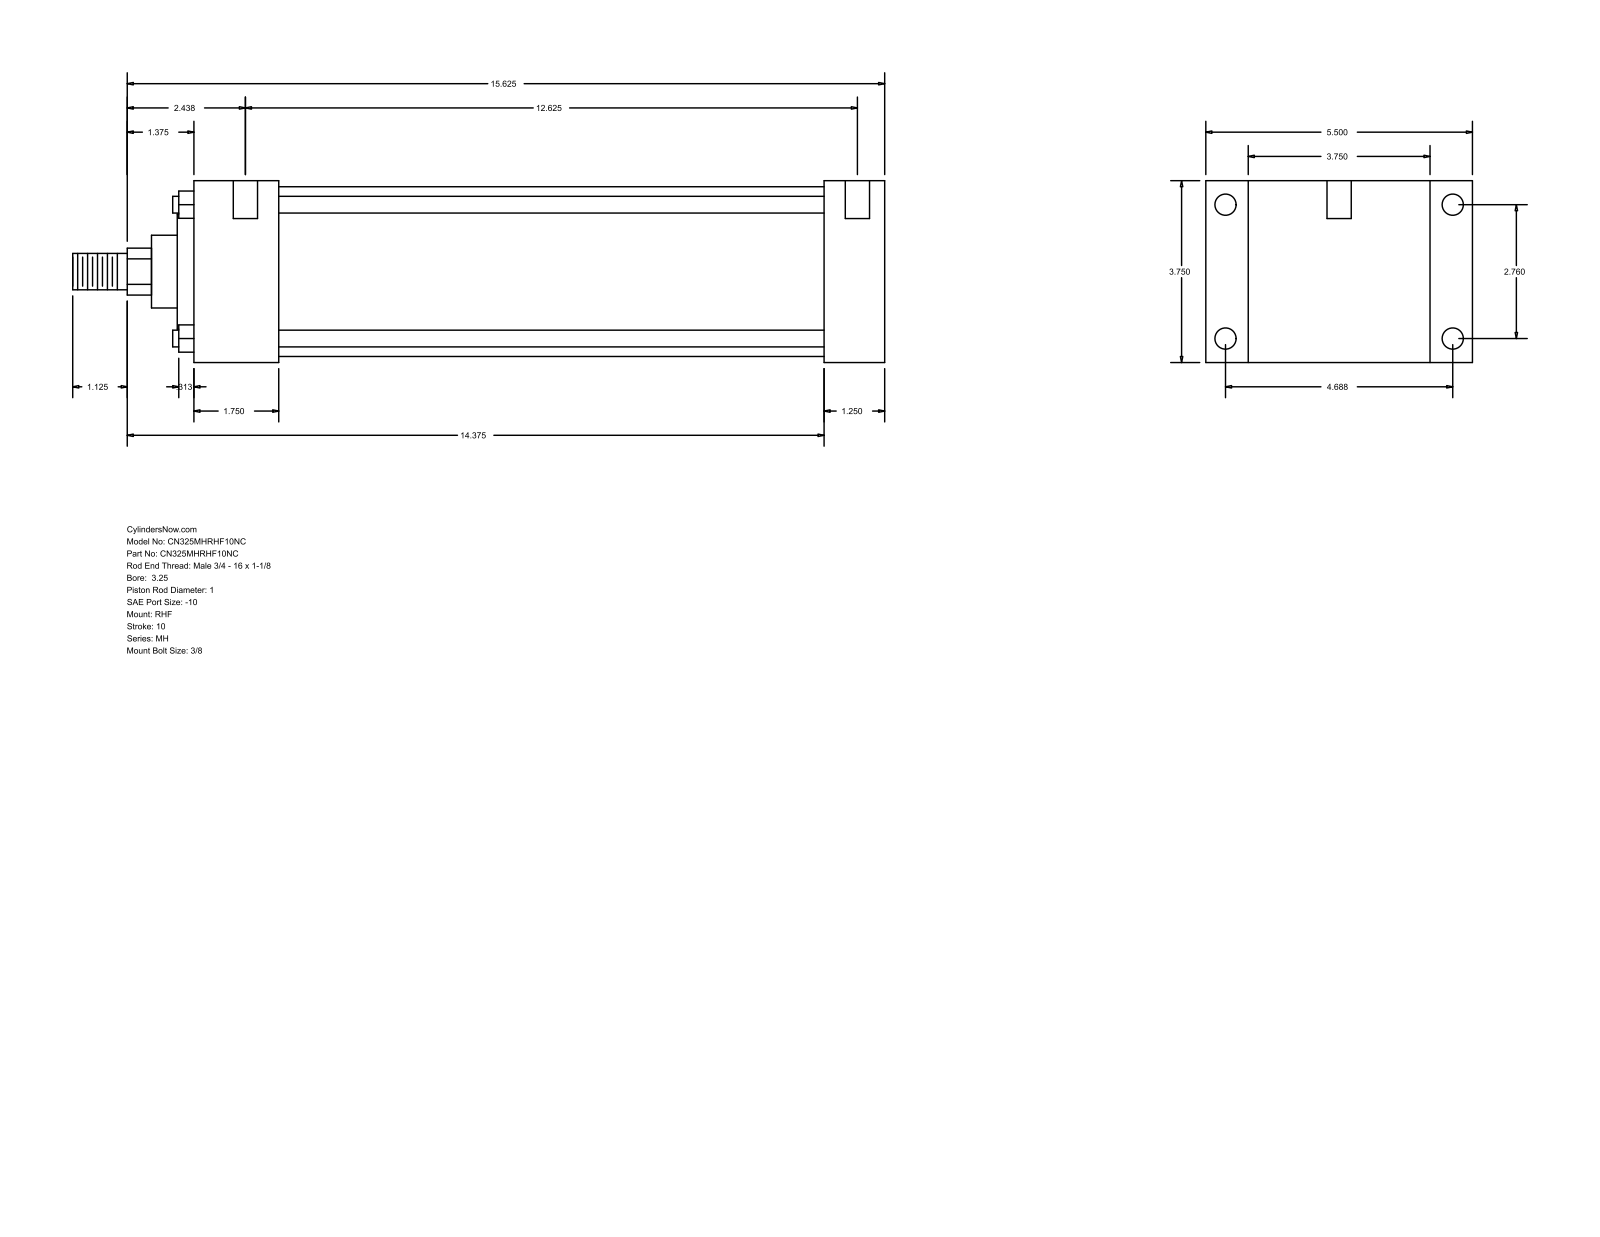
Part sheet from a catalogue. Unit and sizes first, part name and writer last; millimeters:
Units: millimetres
Overall size (bounding box): 425.45 × 139.7 × 95.25
Round holes (diameter × count): ⌀5.56 ×4, ⌀11.13 ×4, ⌀12.7 ×2
Round bosses / shafts (diameter × count): ⌀8.76 ×4, ⌀88.9 ×1, ⌀60.33 ×1, ⌀38.1 ×1, ⌀25.4 ×1, ⌀19.05 ×1
Partial cylindrical surfaces — rounded edges, fillets, slot ends (radius × count): R12.29 ×1
Main face-to-face distances: 95.24, 31.76, 22.23, 117.47, 330.2, 361.96, 139.7, 44.46, 285.74, 317.5
Hole centre spacings: 70.1, 119.06, 138.16, 327.02, 1.58, 4.76, 320.68, 322.26
Bodies: 0 solids, 90 faces (61 planar, 29 cylindrical, 0 other)
Part name (STEP PRODUCT): MH_RHF__0325_1
STEP written by: GSSL Pune (CONFIG_CONTROL_DESIGN)
